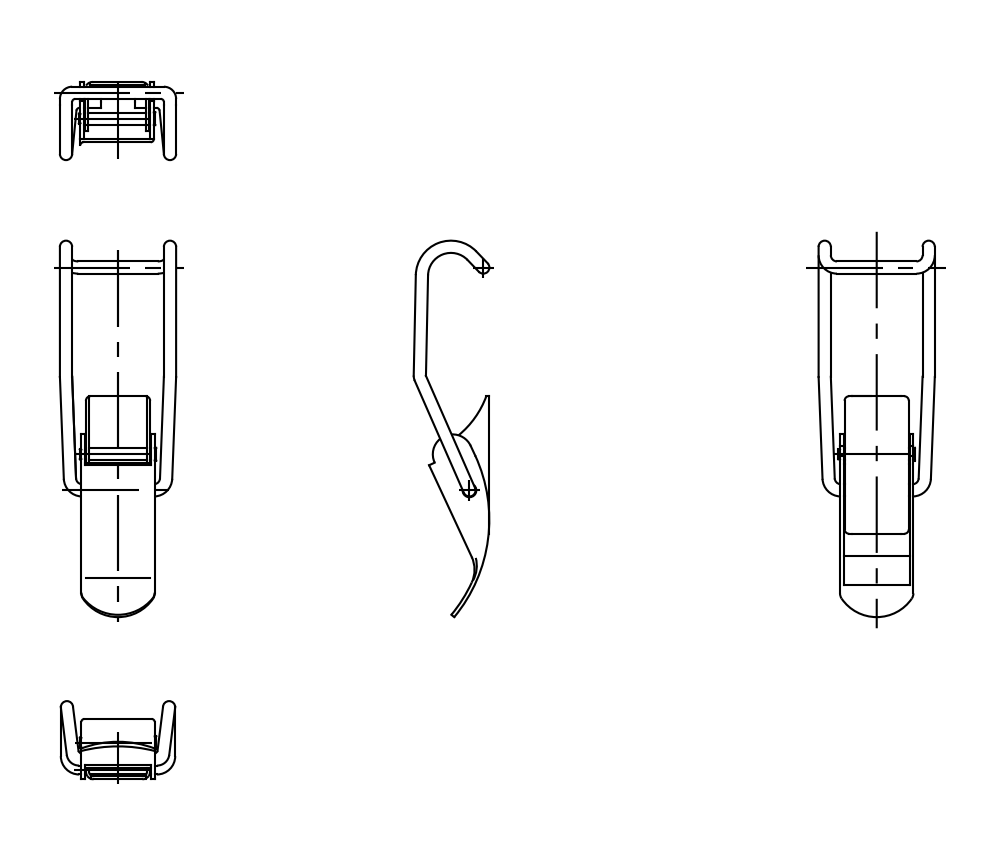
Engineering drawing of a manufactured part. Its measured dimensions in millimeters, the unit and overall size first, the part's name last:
Units: millimetres
Overall size (bounding box): 122.94 × 38 × 25.58
Round holes (diameter × count): ⌀3.1 ×1, ⌀4.1 ×1, ⌀4.2 ×1, ⌀4.5 ×1
Round bosses / shafts (diameter × count): ⌀4 ×9, ⌀3 ×1
Partial cylindrical surfaces — rounded edges, fillets, slot ends (radius × count): R1.5 ×6, R1 ×2, R1.2 ×2, R2.5 ×2, R30 ×2, R4 ×1, R4.5 ×1, R6.5 ×1
Main face-to-face distances: 1, 1.2, 22.8, 1.19, 24, 21.6, 1.5, 22.5, 21.3, 2.5
Hole centre spacings: 13
Volume: 7 392 mm³ · Surface area: 10 982 mm²
Bodies: 4 solids, 103 faces (22 planar, 64 cylindrical, 17 other)
Part name (STEP PRODUCT): レバー; シャフト; ベース; アーム
STEP written by: spGate 19.8.4 (****-****-****-****) (AUTOMOTIVE_DESIGN)
